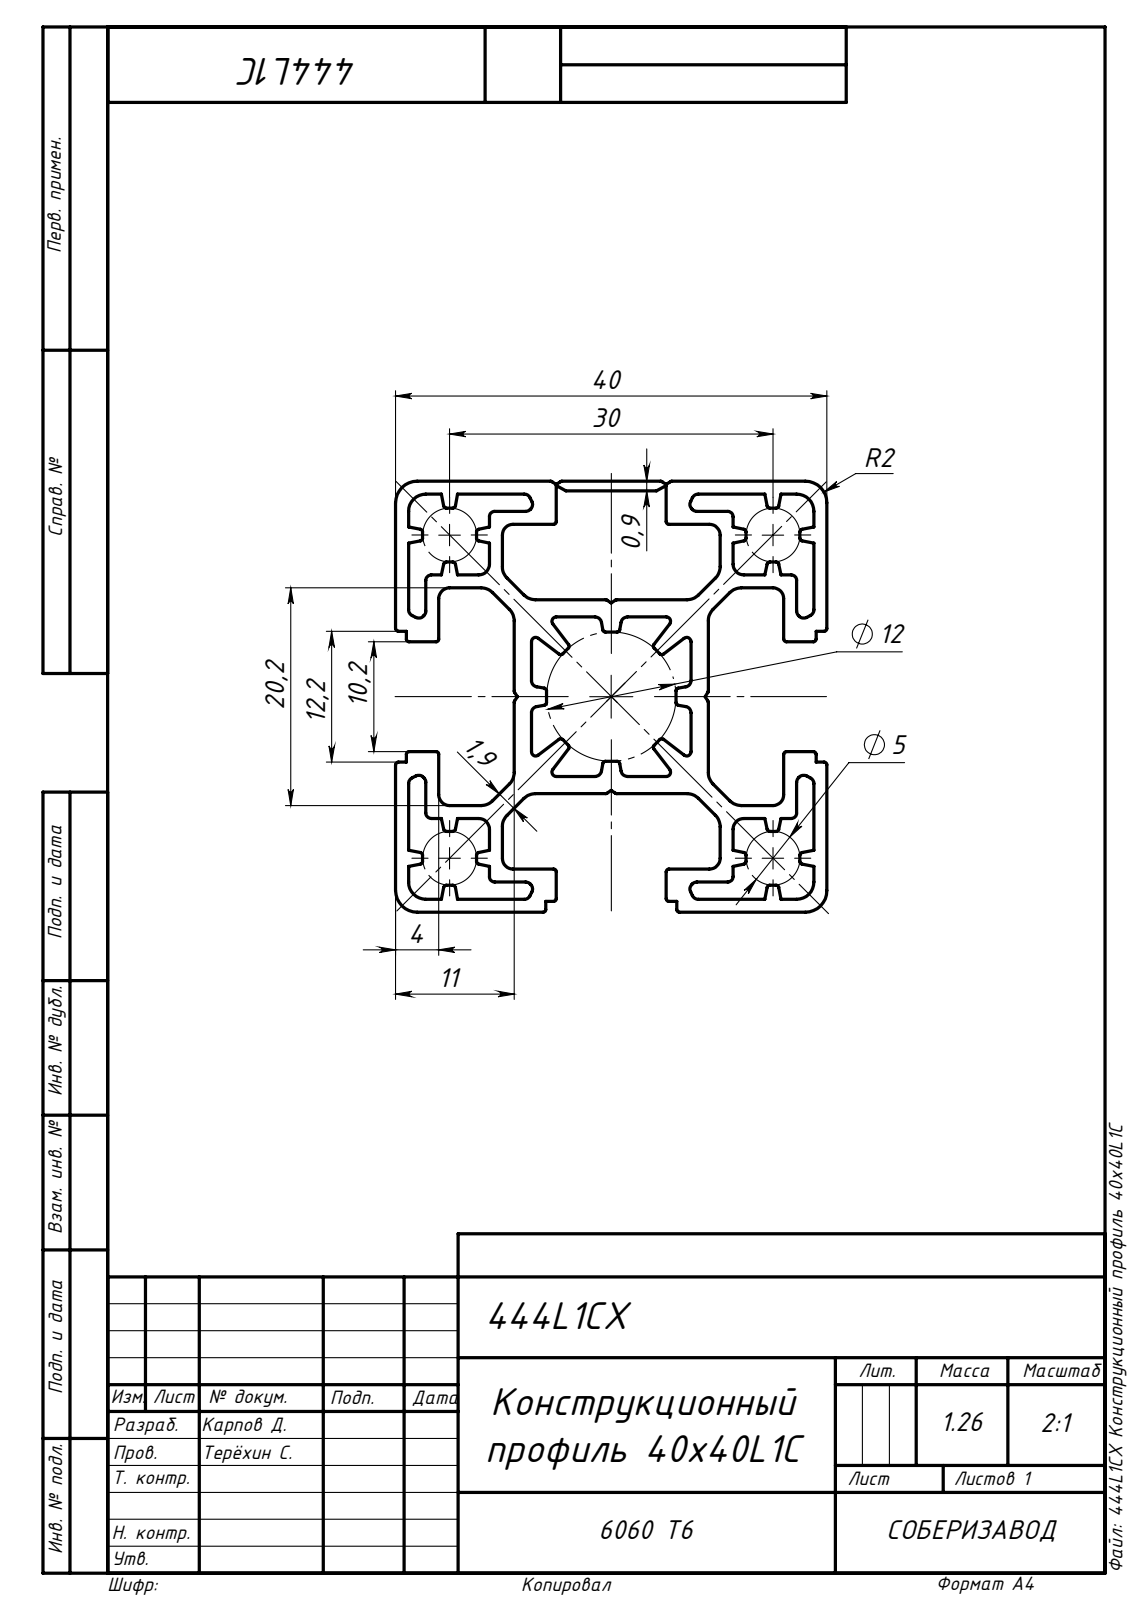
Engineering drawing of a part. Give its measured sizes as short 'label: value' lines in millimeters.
written by: SolidWorks 2019 (AUTOMOTIVE_DESIGN)
unit: mm
bodies: 1 solid, 402 faces (214 planar, 188 cylindrical, 0 other)
size: 1000 × 40 × 40
volume: 468 464 mm³; area: 612 111 mm²
rounds: 80× R0.25, 32× R0.6, 16× R1.5, 12× R1, 8× R0.4, 8× R0.5, 4× R1.6, 4× R2
face distances: 1.2, 9.8, 38.8, 2.8, 36, 11, 29, 27.8, 26.2, 1.6
